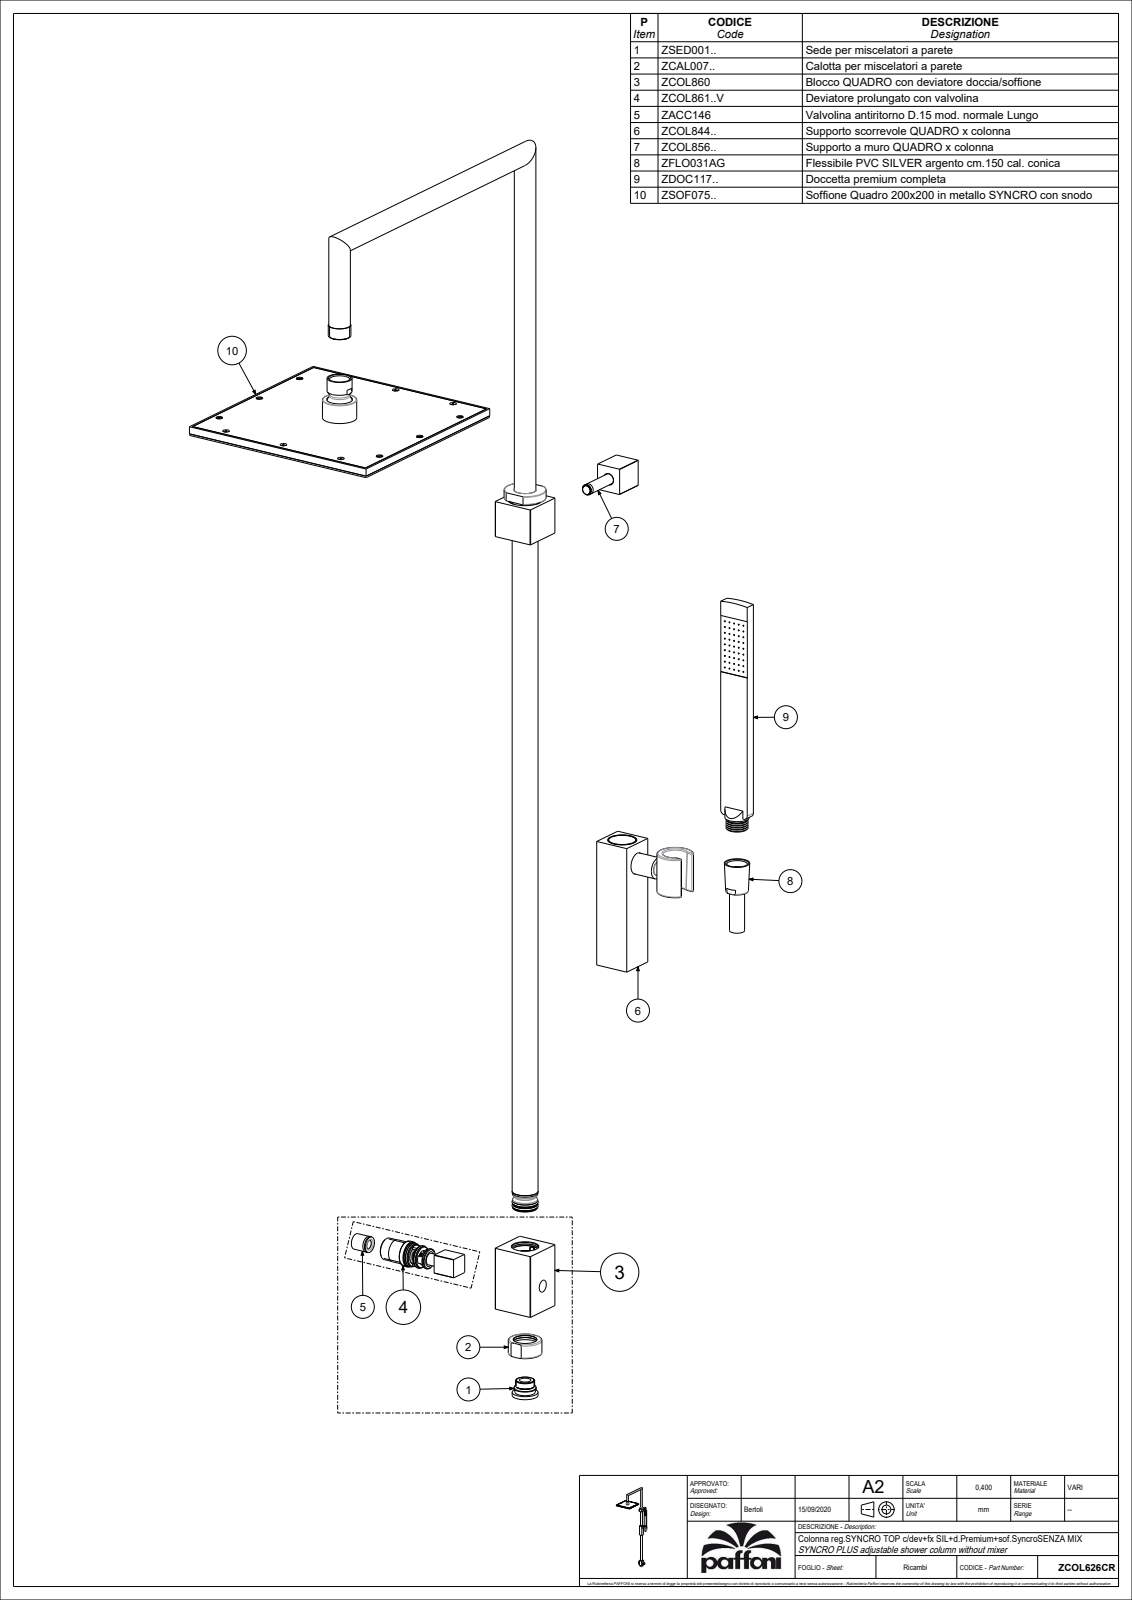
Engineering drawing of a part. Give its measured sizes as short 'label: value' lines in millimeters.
name: ZCOL626CR
written by: CREO PARAMETRIC BY PTC INC, 2020044 (CONFIG_CONTROL_DESIGN)
unit: mm
bodies: 10 solids, 5616 faces (907 planar, 1021 cylindrical, 3688 other)
size: 1035 × 480.1 × 200.2
volume: 684 931 mm³; area: 499 063 mm²
holes: 100× ⌀1.5, 100× ⌀1.7, 13× ⌀7, 12× ⌀2.5, 12× ⌀5.1, 12× ⌀6, 4× ⌀5, 3× ⌀3.3, 3× ⌀10.5, 3× ⌀17, 2× ⌀4.5, 2× ⌀16.5
bosses: 101× ⌀10, 12× ⌀5, 11× ⌀2, 4× ⌀20, 1× ⌀34, 1× ⌀31.8, 1× ⌀28, 1× ⌀27.5
rounds: 12× R20, 8× R1, 4× R12, 2× R4, 1× R6.75, 1× R12.1, 1× R12.3, 1× R12.32
face distances: 8.5, 7.5, 1, 7, 6, 1.5, 3, 37, 25, 22
hole spacings: 16.3, 36.45, 23.05, 51.55, 32.6, 67.21, 48.9, 65.2
